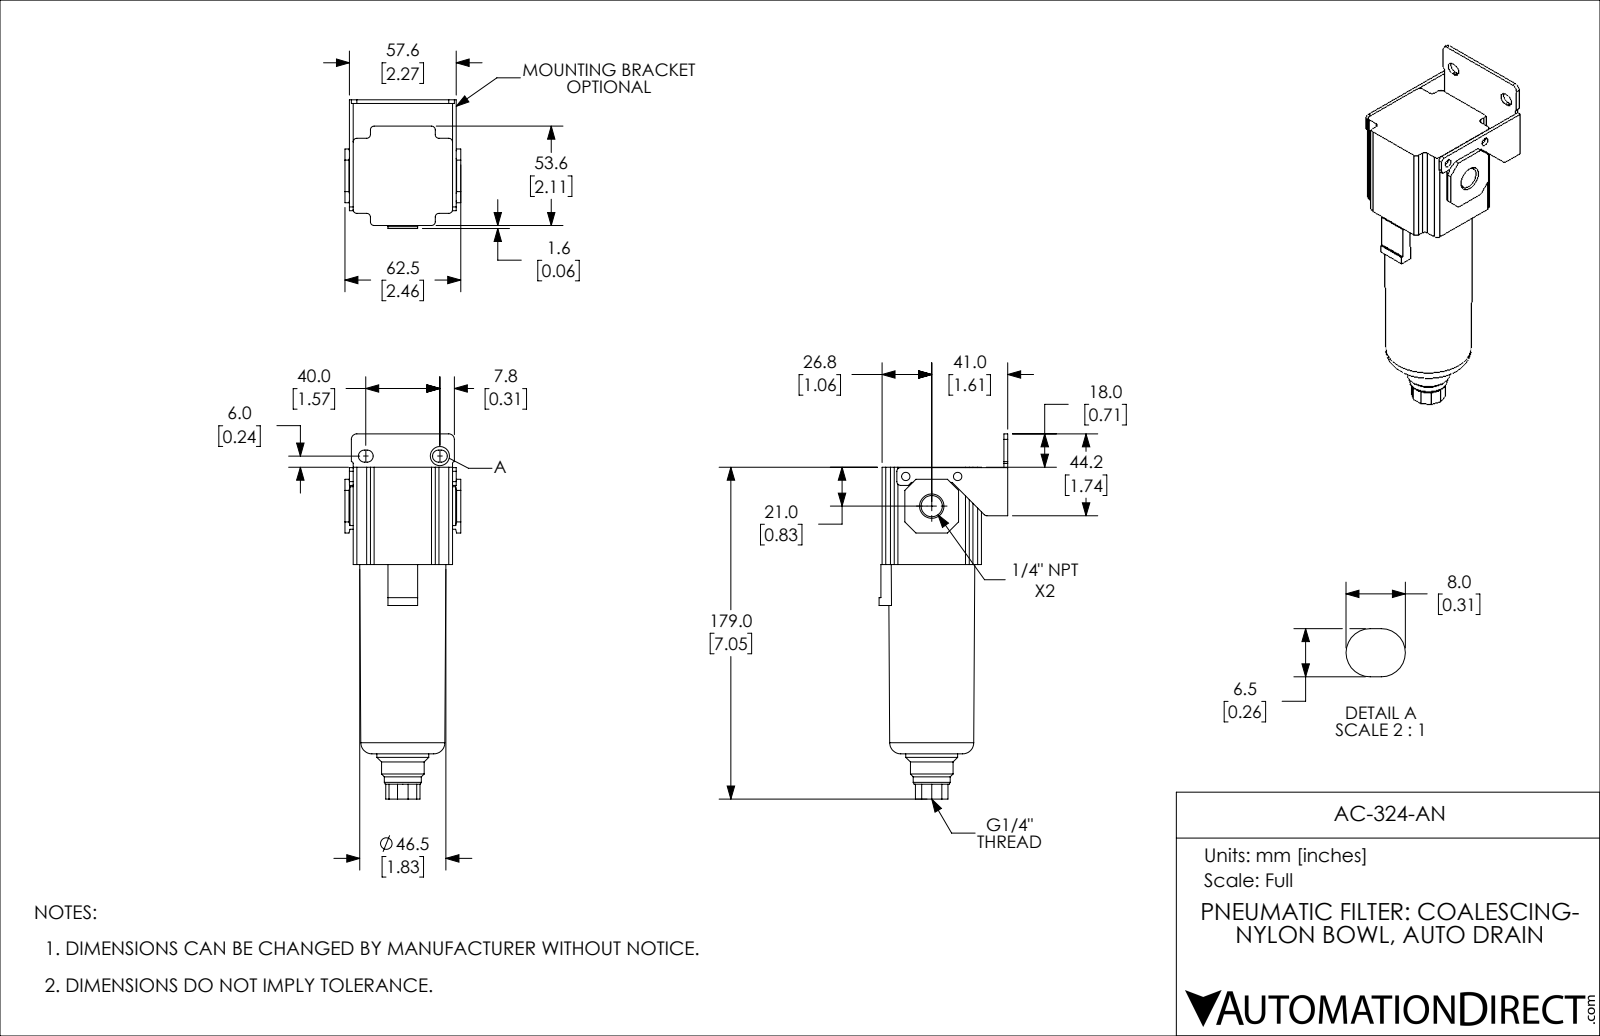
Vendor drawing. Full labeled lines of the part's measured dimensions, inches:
Part name (STEP PRODUCT): AC-324-AN
STEP written by: SolidWorks 2018 (AUTOMOTIVE_DESIGN)
Units: inches
Bodies: 1 solid, 173 faces (109 planar, 48 cylindrical, 16 other)
Overall size (bounding box): 7.756 × 2.733 × 2.461
Volume: 20 in³ · Surface area: 65.25 in²
Round holes (diameter × count): ⌀0.177 ×2, ⌀0.451 ×2
Round bosses / shafts (diameter × count): ⌀1.102 ×1, ⌀0.906 ×1, ⌀0.787 ×1
Partial cylindrical surfaces — rounded edges, fillets, slot ends (radius × count): R0.079 ×15, R0.128 ×4, R0.039 ×2, R0.118 ×2
Main face-to-face distances: 0.079, 2.11, 2.189, 0.559, 2.669, 0.48, 2.591, 0.096, 0.175, 2.285
Hole centre spacings: 0.837, 1.102
